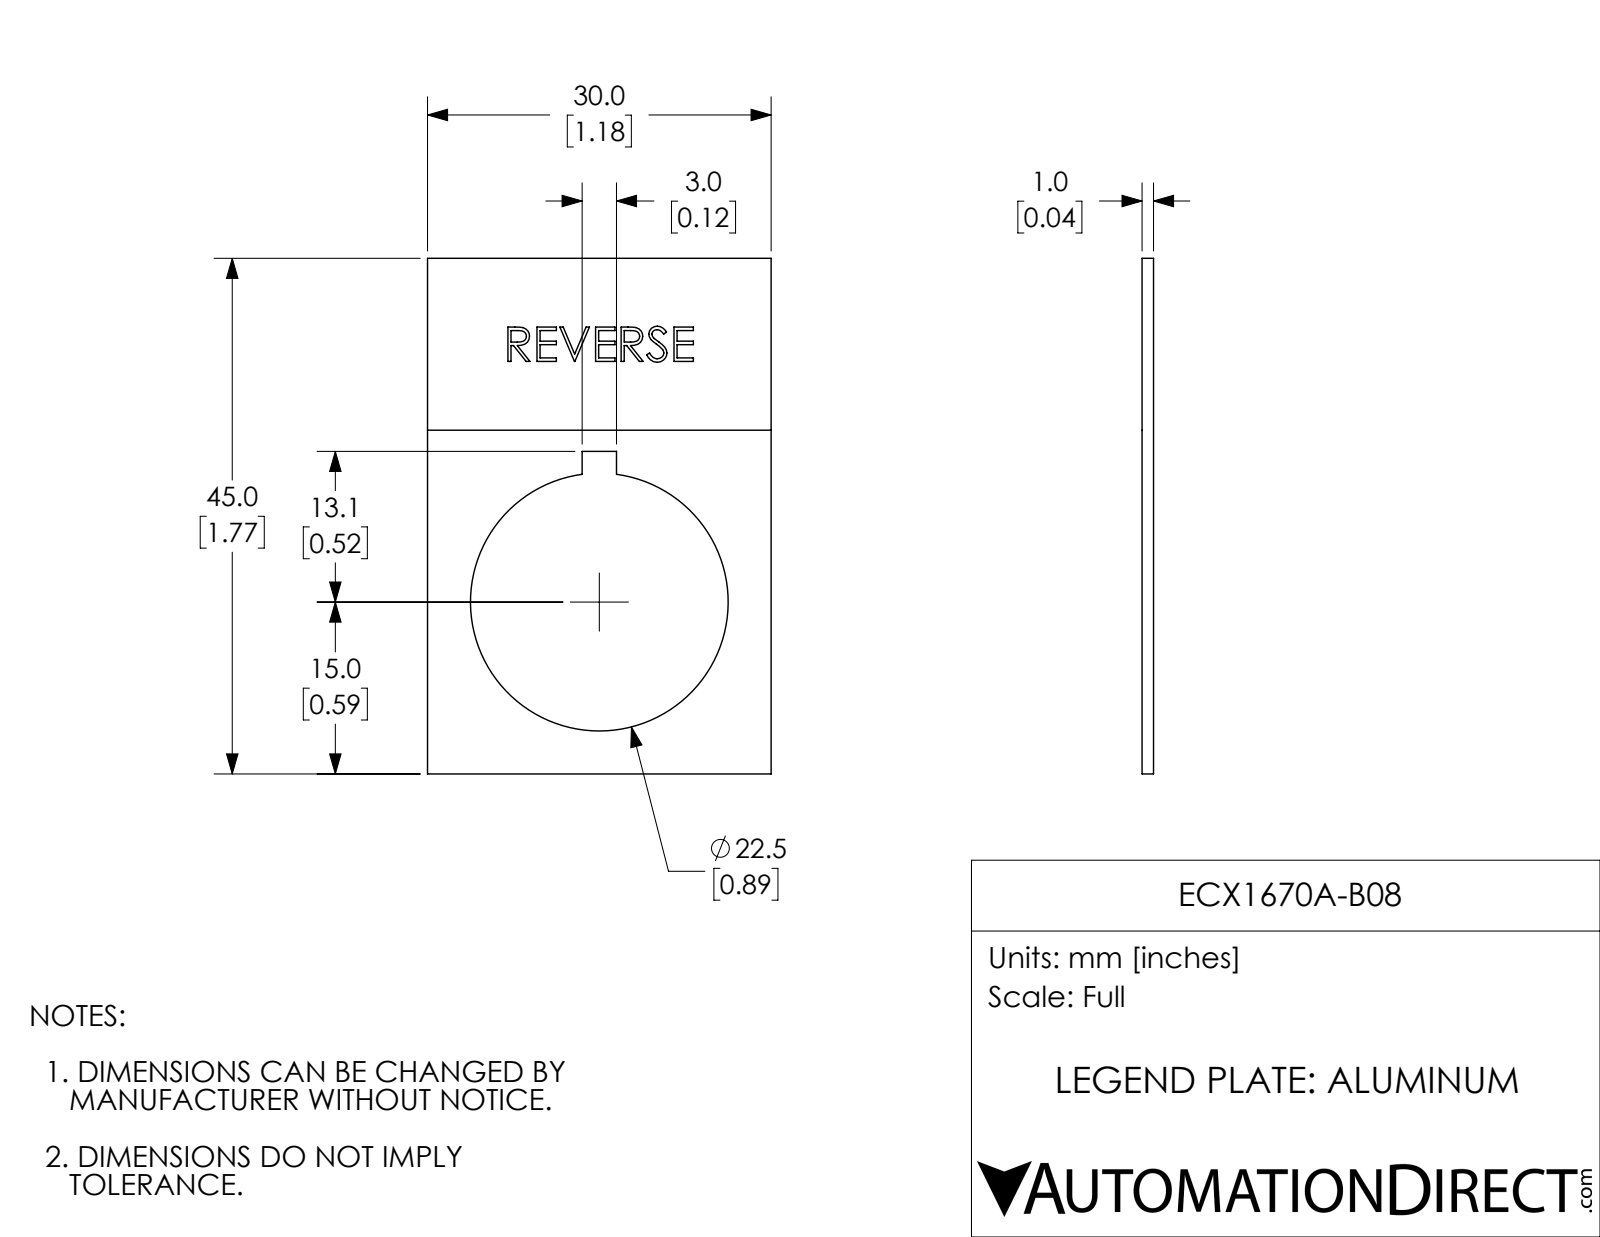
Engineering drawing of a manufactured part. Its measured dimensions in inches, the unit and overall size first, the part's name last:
Units: inches
Overall size (bounding box): 1.772 × 1.181 × 0.039
Round holes (diameter × count): ⌀0.886 ×1
Main face-to-face distances: 0.039, 1.181, 1.772, 0.038, 0.531, 0.65, 1.108, 0.663, 0.118, 0.012
Volume: 0.058 in³ · Surface area: 3.287 in²
Bodies: 1 solid, 114 faces (86 planar, 3 cylindrical, 25 other)
Part name (STEP PRODUCT): ECX1670A-B08
STEP written by: SolidWorks 2017 (AUTOMOTIVE_DESIGN)
